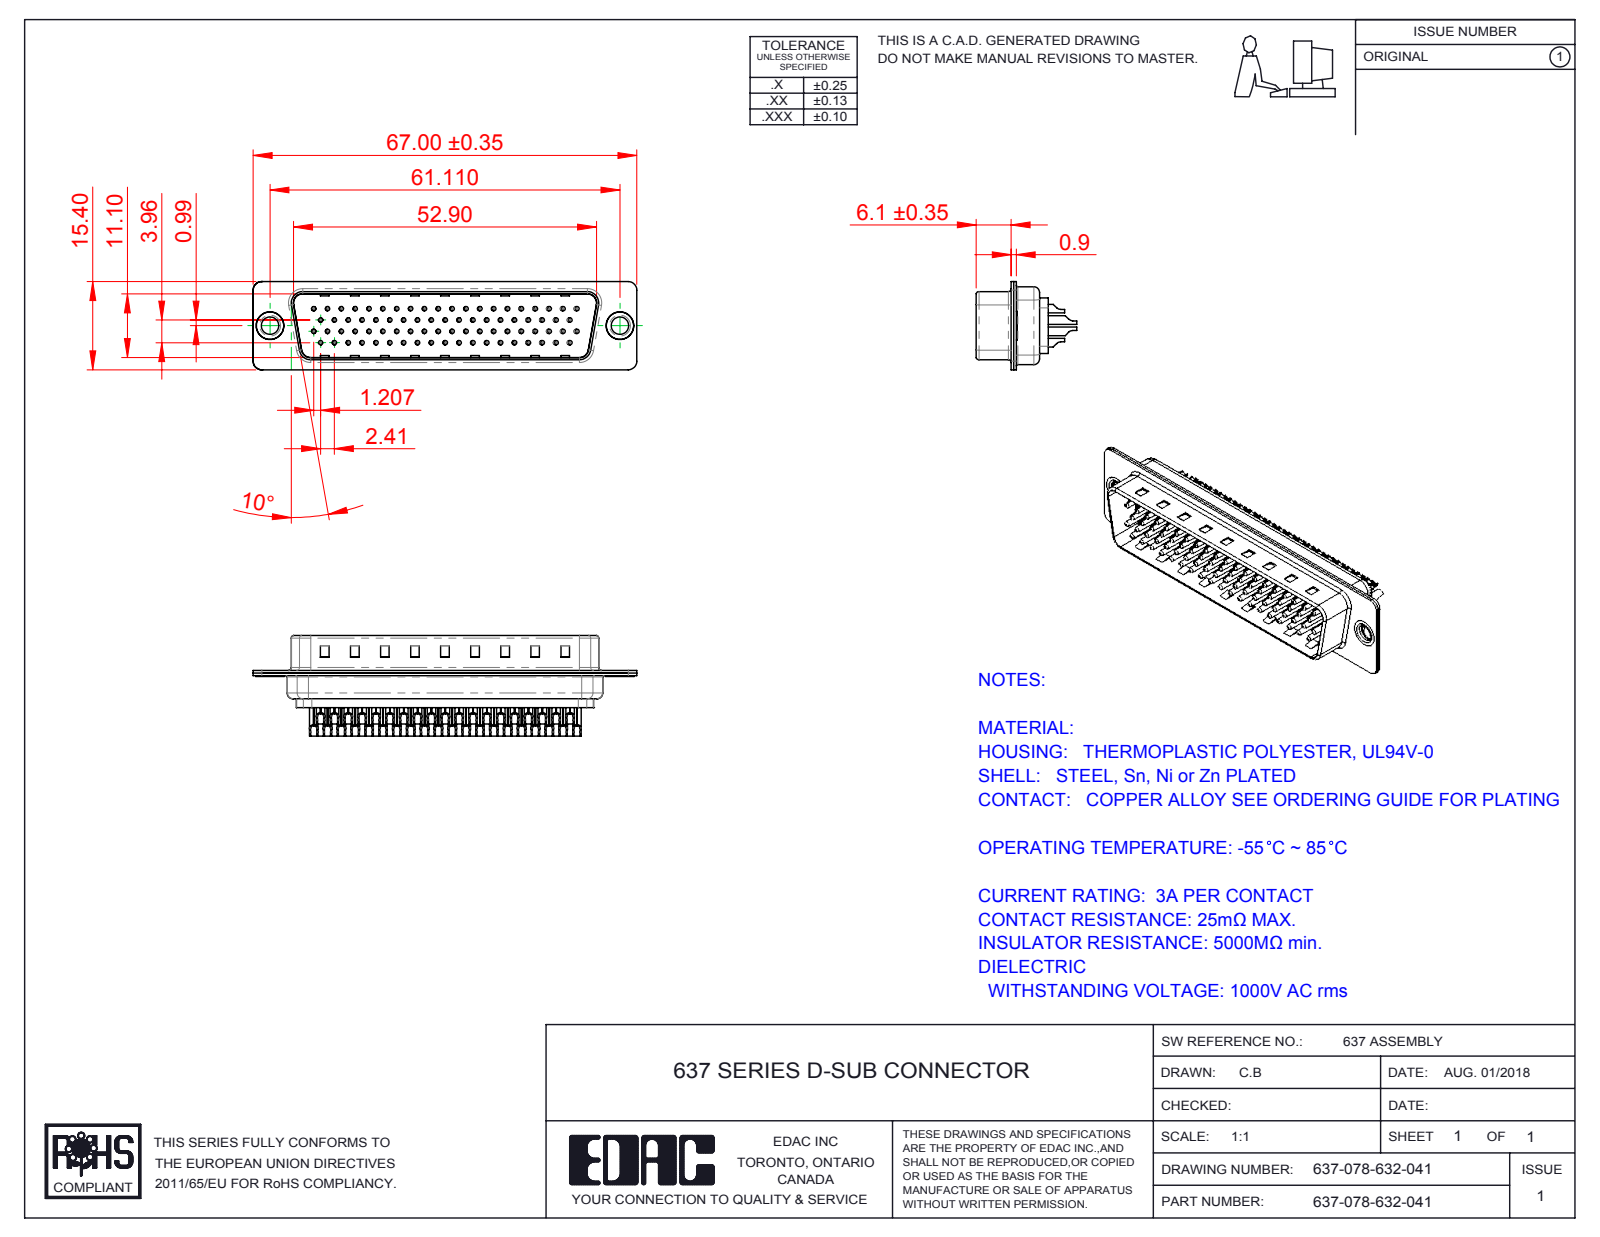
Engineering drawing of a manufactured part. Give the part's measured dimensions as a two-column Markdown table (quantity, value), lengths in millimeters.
| quantity | value |
| --- | --- |
| part name | 637 Housing_78 Contacts; 637-078-632-041; 637 Contact Row 3_32; 637 Contact Row 78_32 (+5 more) |
| STEP written by | SolidWorks 2016 (CONFIG_CONTROL_DESIGN) |
| units | millimeters |
| bodies | 83 solids, 5378 faces (1295 planar, 2387 cylindrical, 1696 other) |
| overall size | 67 × 17.55 × 15.4 |
| volume | 4 356 mm³ |
| surface area | 16 633 mm² |
| round holes (diameter × count) | 1.6 × 150, 0.35 × 78, 1.1 × 78, 0.75 × 72, 2 × 72, 4 × 3, 3.05 × 2, 4.8 × 2 |
| round bosses / shafts (diameter × count) | 2 × 78, 1.5 × 78, 0.75 × 78, 5 × 2, 4.9 × 2, 3.55 × 2, 4.8 × 1 |
| partial cylindrical surfaces (radius × count) | 1.5 × 16, 2 × 12, 0.5 × 8, 1 × 8, 0.25 × 4, 0.55 × 4, 0.7 × 4, 0.95 × 4 |
| main face-to-face distances | 0.45, 0.4, 1.5, 1.95, 11.9, 11.5, 0.7, 11.1, 0.9, 0.8 |
| hole center spacings | 2.41, 7.24, 6.06, 9.65, 6.96, 8.46, 14.54, 16.89 |
